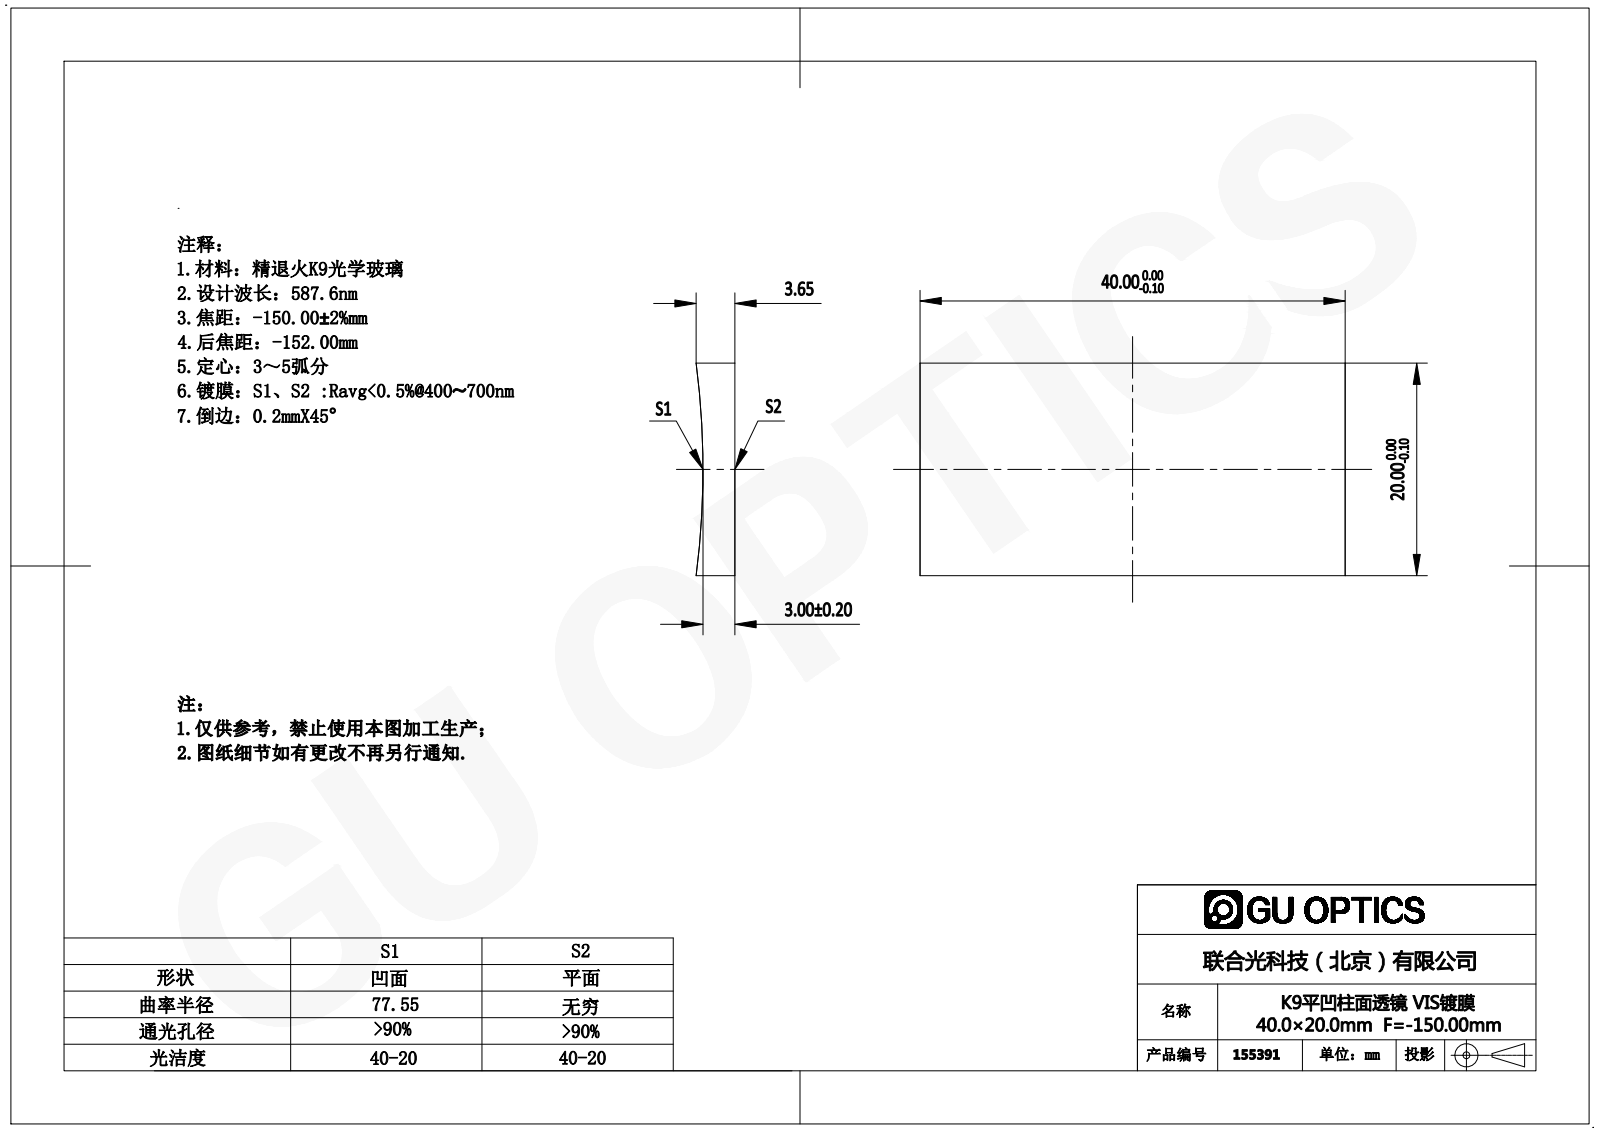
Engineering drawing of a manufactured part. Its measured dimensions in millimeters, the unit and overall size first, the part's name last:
Units: millimetres
Overall size (bounding box): 40 × 20 × 3.65
Partial cylindrical surfaces — rounded edges, fillets, slot ends (radius × count): R77.55 ×1
Main face-to-face distances: 20, 40
Volume: 2 572 mm³ · Surface area: 2 023 mm²
Bodies: 1 solid, 6 faces (5 planar, 1 cylindrical, 0 other)
Part name (STEP PRODUCT): 155358
STEP written by: SolidWorks 2016 (AUTOMOTIVE_DESIGN)
